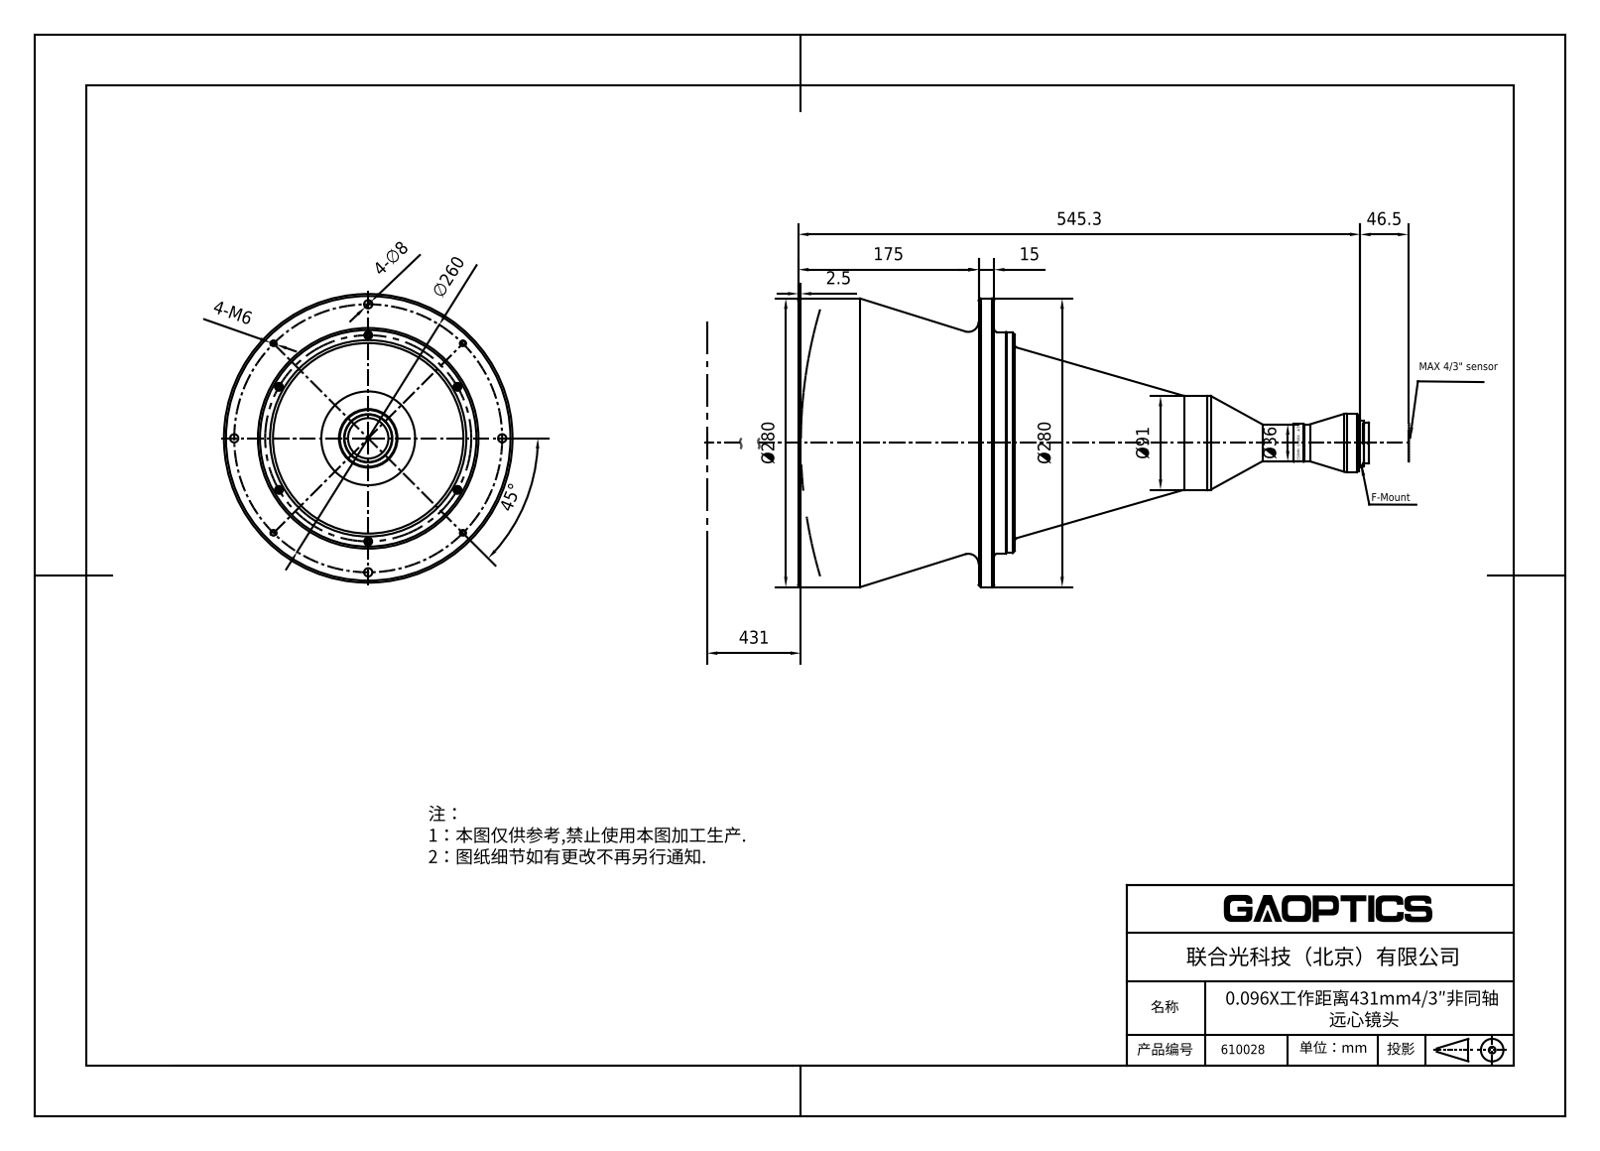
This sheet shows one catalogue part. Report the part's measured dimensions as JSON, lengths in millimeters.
{"part_name": "610028", "step_written_by": "SolidWorks 2020 (CONFIG_CONTROL_DESIGN)", "units": "millimeters", "bodies": {"solids": 0, "faces": 1181, "planar": 418, "cylindrical": 243, "other": 520}, "overall_size": [553.27, 280, 280], "round_holes": [[7, 6], [2, 3], [2.2, 3], [3, 3], [1.4, 1], [7.9, 1], [11.4, 1], [14, 1], [14.6, 1], [15.2, 1], [15.8, 1], [16, 1]], "round_bosses_or_shafts": [[7.5, 6], [8, 4], [5, 4], [2.8, 3], [2, 3], [267.03, 1], [265.8, 1], [256.2, 1]], "partial_cylinders_radius": [[0.5, 6], [0.75, 2], [1, 1], [18.1, 1], [18.2, 1], [22.95, 1]], "face_to_face_distances": [165.26, 150.26, 15, 185.26, 35, 20, 24.74, 175, 190, 210], "hole_center_spacings": [100, 25.5, 103.2, 173.2, 44.17, 78.95, 122.74, 1.33]}
